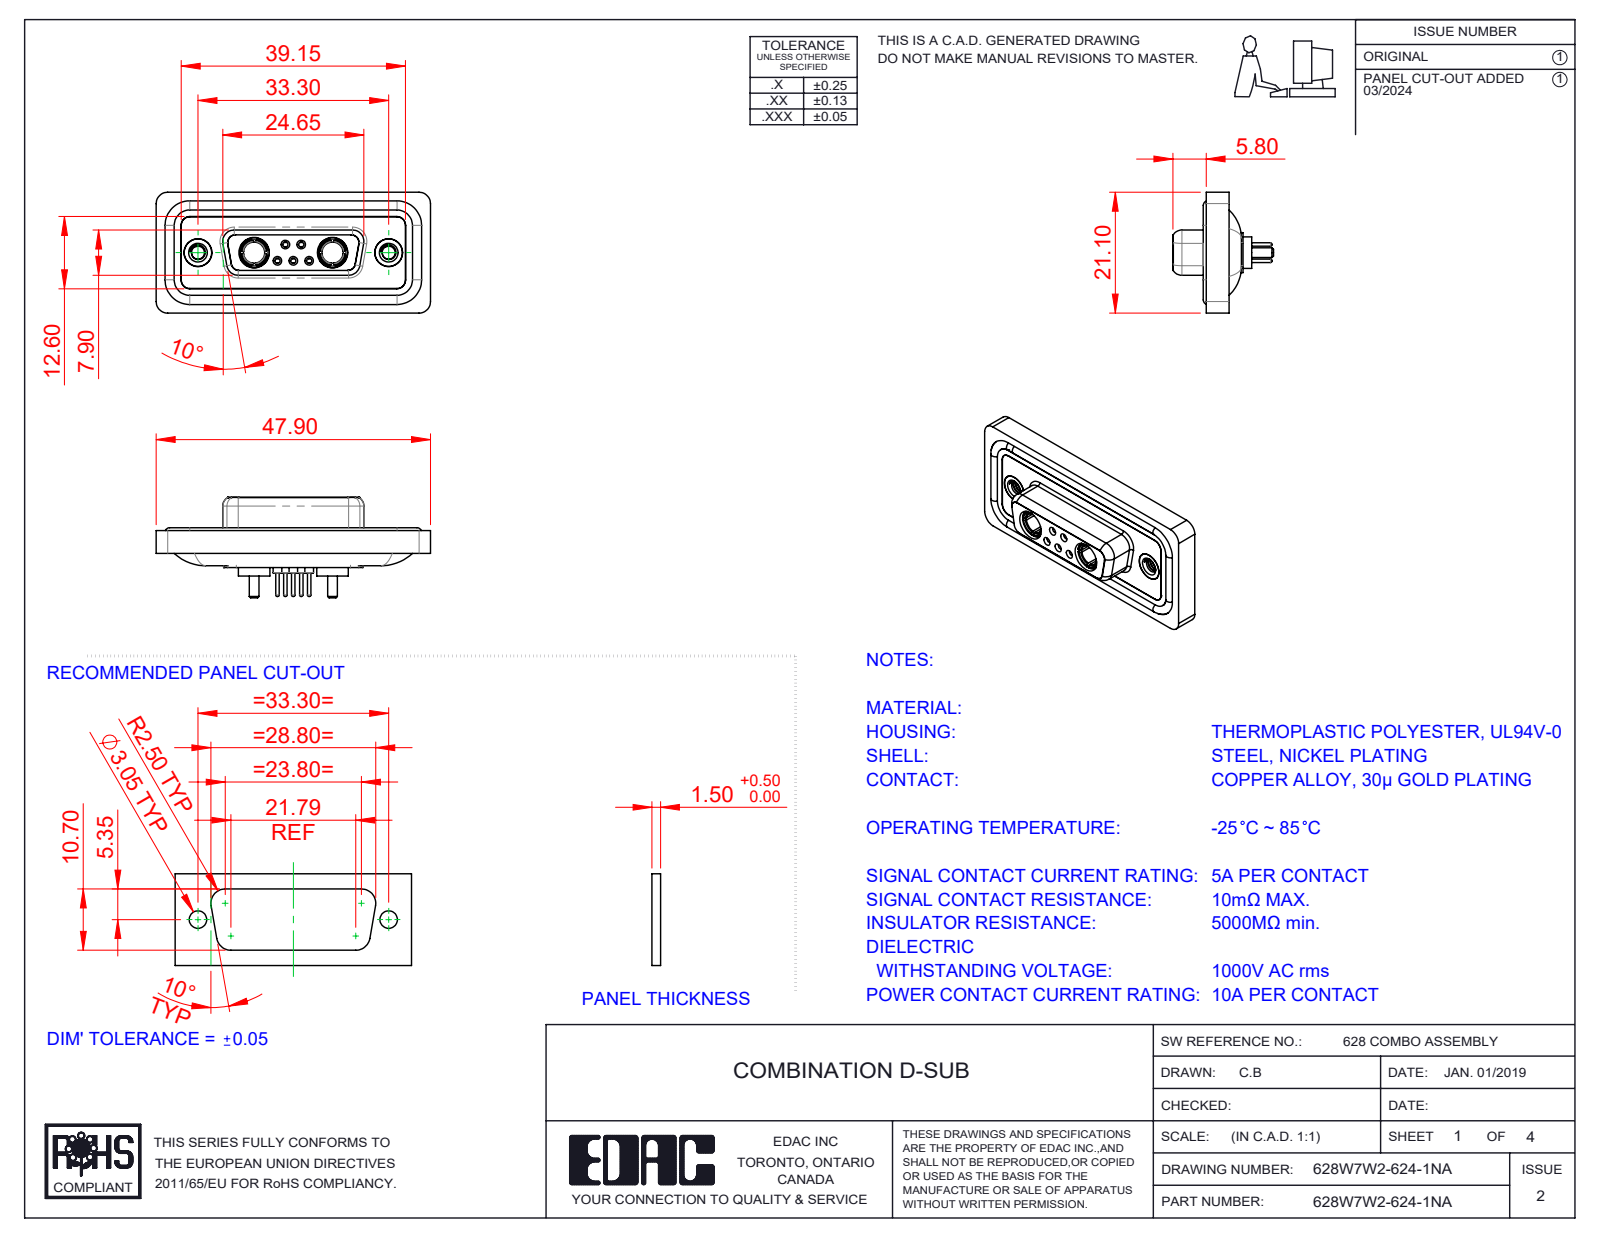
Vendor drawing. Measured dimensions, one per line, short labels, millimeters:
name: 628Combo Contact Row 1_24; 628Combo Waterproof Housing_15 Contacts; 628Combo Shell Front_15 Contacts; Power Socket_10A S (+5 more)
written by: SolidWorks 2023 (CONFIG_CONTROL_DESIGN)
unit: mm
bodies: 16 solids, 807 faces (238 planar, 331 cylindrical, 238 other)
size: 47.9 × 21.1 × 17.55
volume: 6 049 mm³; area: 9 857 mm²
holes: 5× ⌀0.9, 5× ⌀1.1, 5× ⌀1.5, 5× ⌀2, 4× ⌀4.85, 3× ⌀1.6, 2× ⌀1.7, 2× ⌀2.26, 2× ⌀3.7, 2× ⌀4, 2× ⌀4.05, 2× ⌀5
bosses: 6× ⌀1.6, 5× ⌀2.2, 5× ⌀0.6, 2× ⌀5.5, 2× ⌀5.2, 2× ⌀4.96, 2× ⌀4.95, 2× ⌀4.8
rounds: 22× R1.5, 20× R2, 12× R1.35, 8× R1.6, 4× R0.25, 4× R0.5, 4× R0.6, 4× R0.65
face distances: 0.4, 1.8, 1.6, 0.5, 2.9, 1.1, 7.45, 5.65, 6.6, 7.05
hole spacings: 3.16, 2.77, 9.8, 23.5, 4.31, 4.33, 5.03, 5.04
